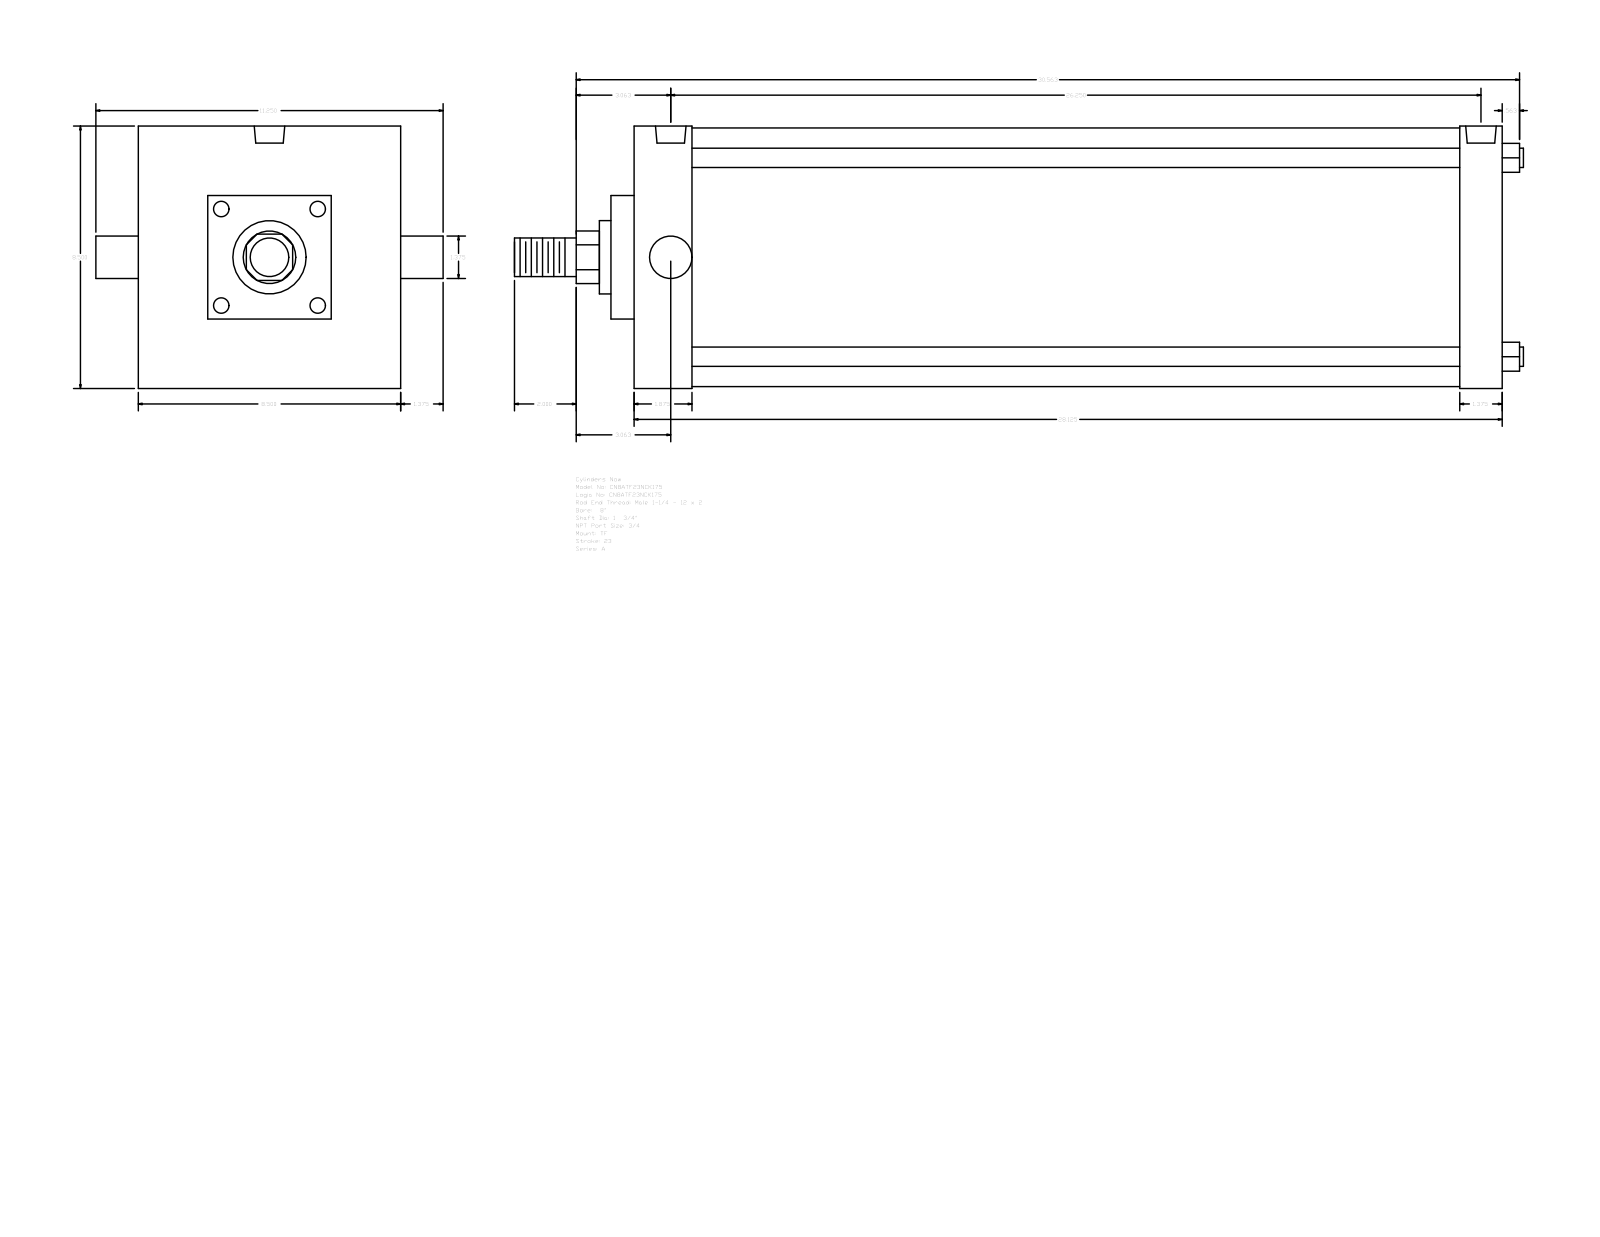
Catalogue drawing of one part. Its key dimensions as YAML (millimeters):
part_name: "A_TF__0800_1.75"
step_written_by: "GSSL Pune (CONFIG_CONTROL_DESIGN)"
units: millimeters
bodies: {solids: 0, faces: 89, planar: 65, cylindrical: 24, other: 0}
overall_size: [830.26, 285.75, 215.9]
round_holes:
  - {diameter: 15.08, count: 3}
  - {diameter: 25.12, count: 2}
round_bosses_or_shafts:
  - {diameter: 15.88, count: 4}
  - {diameter: 212.72, count: 1}
  - {diameter: 60.33, count: 1}
  - {diameter: 44.45, count: 1}
  - {diameter: 34.92, count: 1}
  - {diameter: 31.75, count: 1}
partial_cylinders:
  - {radius: 21.63, count: 1}
face_to_face_distances: [714.38, 215.9, 47.63, 666.75, 679.46, 631.83, 34.92, 19.05, 57.15, 158.75]
hole_center_spacings: [6.35, 660.4, 654.05, 666.75]
